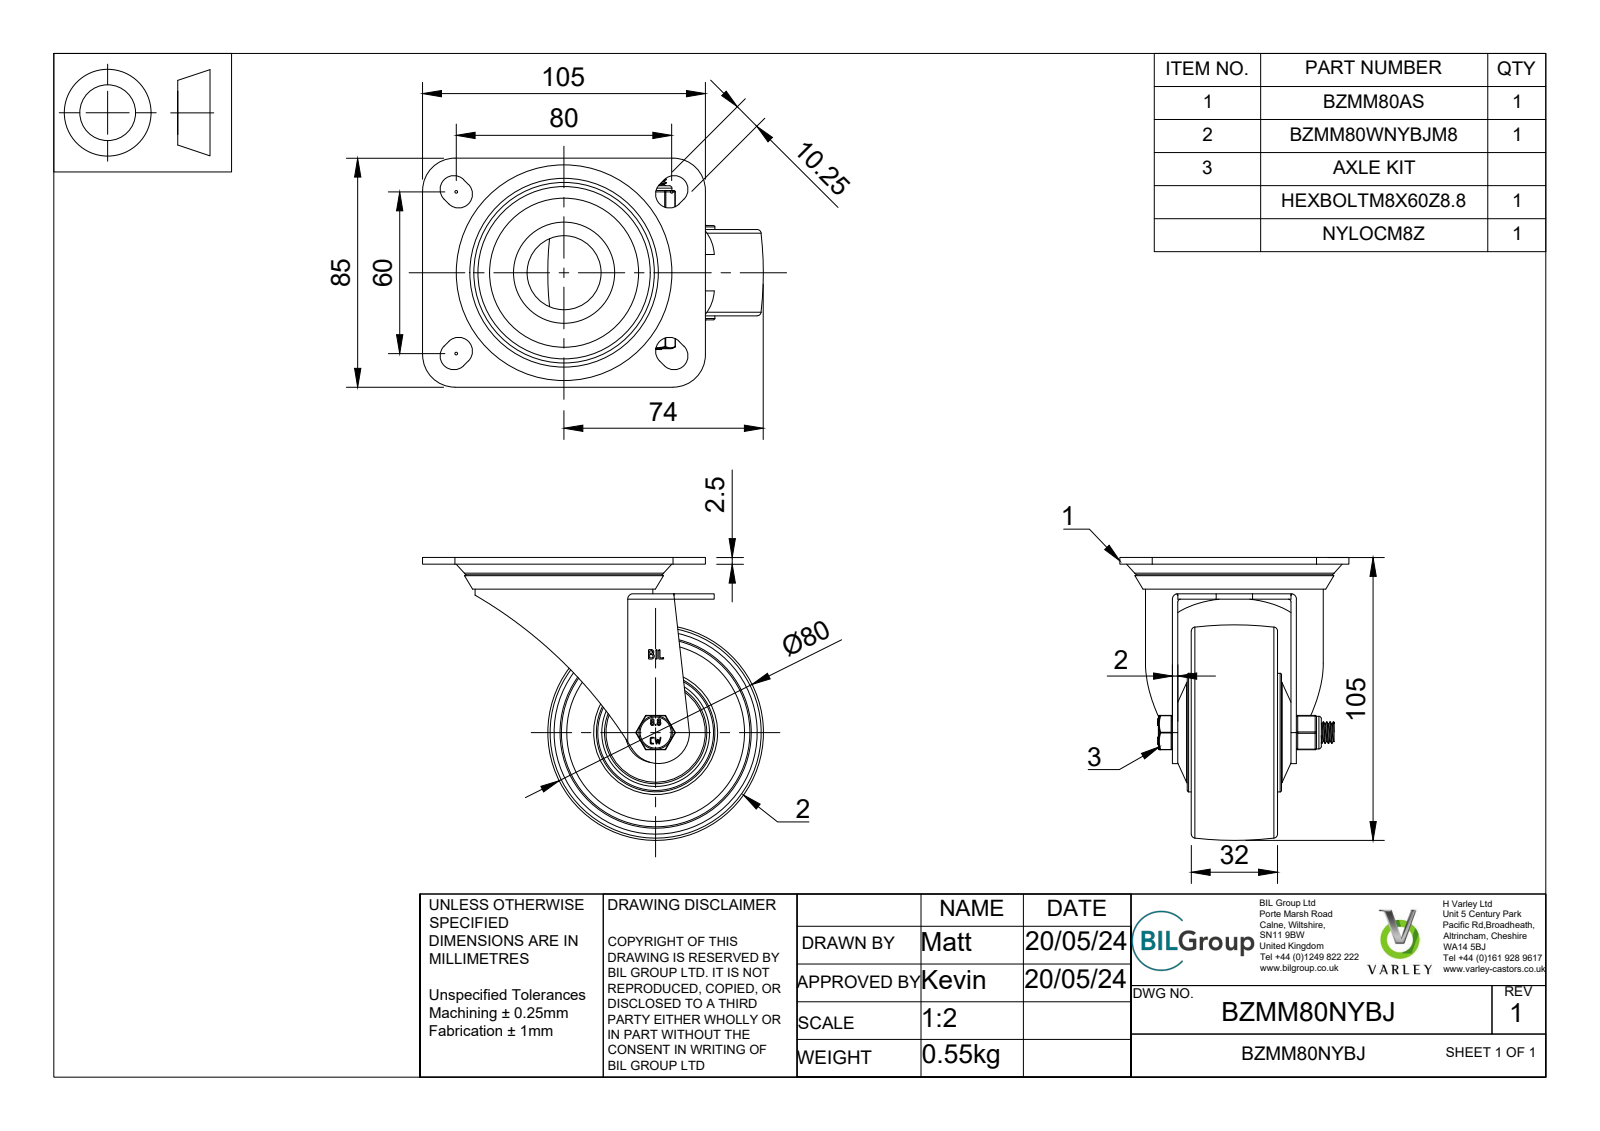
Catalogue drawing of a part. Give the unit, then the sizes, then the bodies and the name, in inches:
Units: inches
Overall size (bounding box): 4.98 × 4.134 × 3.346
Round holes (diameter × count): ⌀0.026 ×2, ⌀0.315 ×1, ⌀0.323 ×1, ⌀0.339 ×1, ⌀0.591 ×1, ⌀0.787 ×1, ⌀0.886 ×1, ⌀0.984 ×1, ⌀1.083 ×1, ⌀1.181 ×1, ⌀1.22 ×1, ⌀1.26 ×1
Round bosses / shafts (diameter × count): ⌀2.598 ×1, ⌀1.732 ×1, ⌀1.496 ×1, ⌀1.24 ×1, ⌀1.201 ×1, ⌀1.102 ×1, ⌀0.906 ×1, ⌀0.748 ×1
Partial cylindrical surfaces — rounded edges, fillets, slot ends (radius × count): R0.02 ×18, R0.01 ×12, R0.202 ×8, R0.472 ×5, R0.013 ×4, R0.025 ×4, R0.039 ×4, R0.025 ×2
Main face-to-face distances: 0.098, 0.079, 0.512, 1.024, 0.413, 0.433, 0.709, 0.197, 0.236, 0.335
Hole centre spacings: 0.183, 0.098
Volume: 8.467 in³ · Surface area: 155 in²
Bodies: 46 solids, 770 faces (274 planar, 193 cylindrical, 303 other)
Part name (STEP PRODUCT): BZMM80NYBJ v3; BZMM80WNYBJM8 v1; BZMM80WNYBJ; NYLON WHEEL (+7 more)
STEP written by: Autodesk Translation Framework v13.14.0.145 (AUTOMOTIVE_DESIGN)
